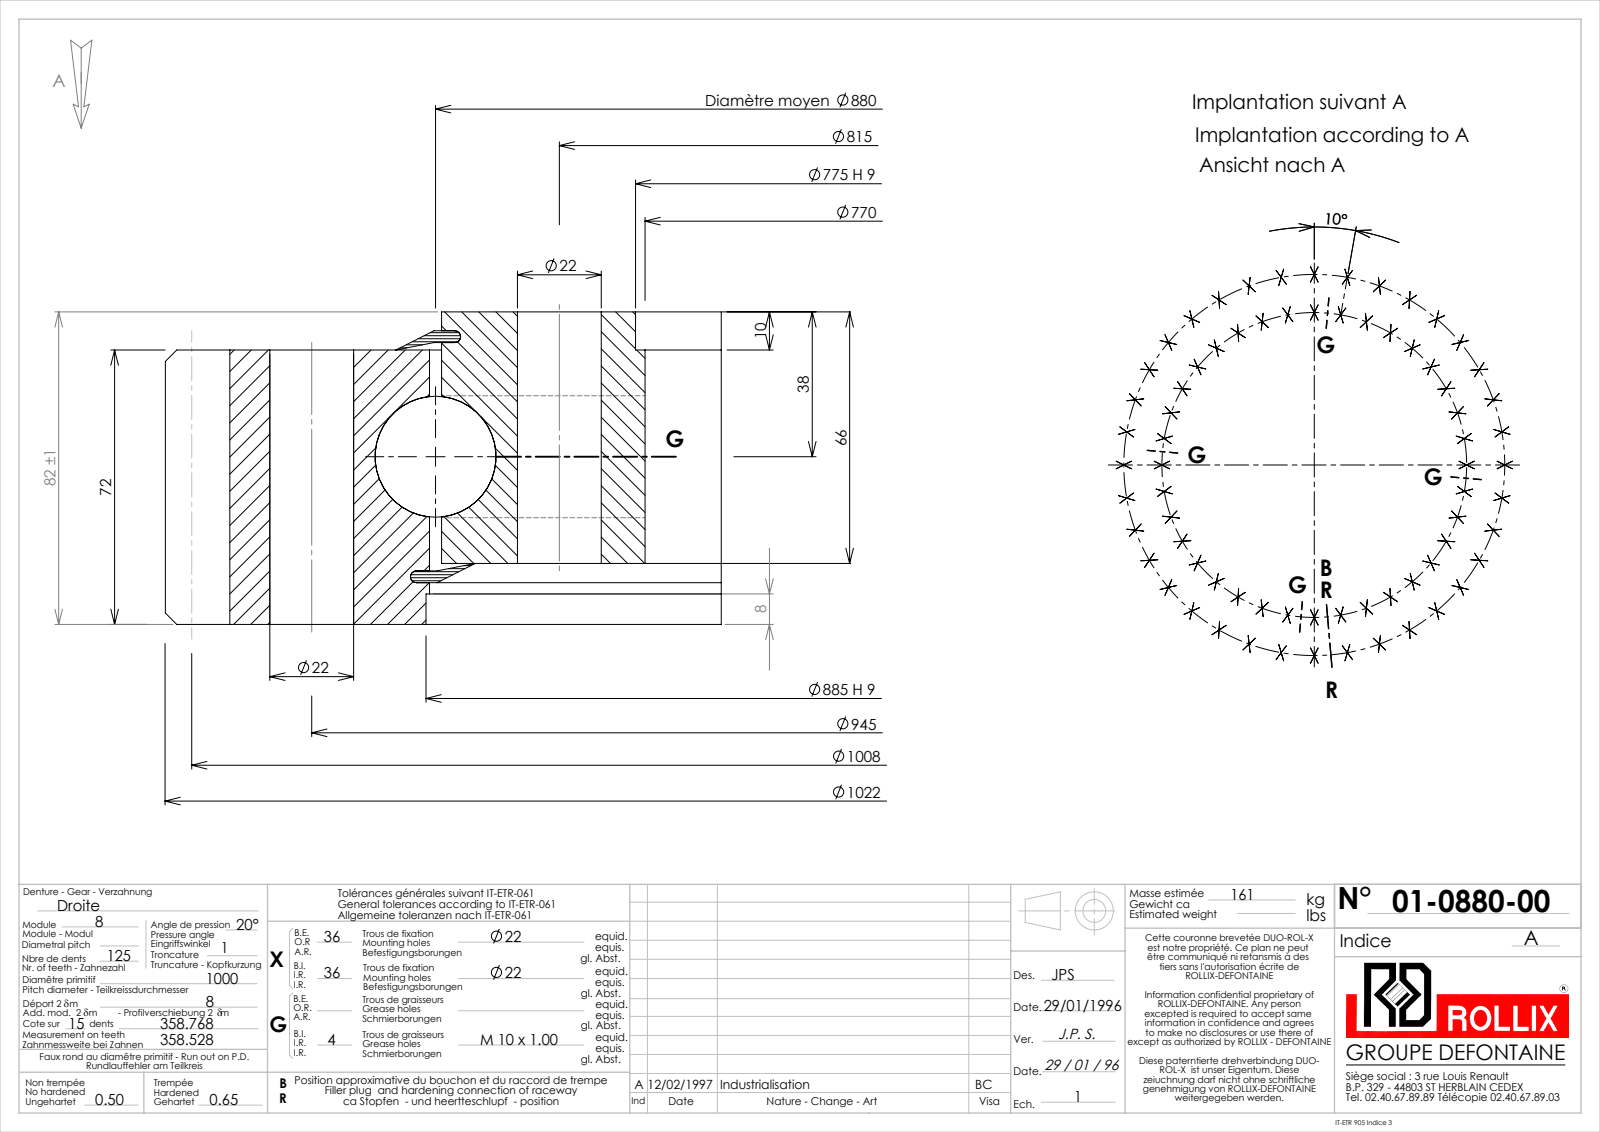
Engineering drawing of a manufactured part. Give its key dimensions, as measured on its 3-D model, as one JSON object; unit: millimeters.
{"part_name": "01-0880-00", "step_written_by": "SolidWorks 2016 (CONFIG_CONTROL_DESIGN)", "units": "millimeters", "bodies": {"solids": 5, "faces": 964, "planar": 264, "cylindrical": 421, "other": 279}, "overall_size": [1021.99, 1021.92, 82], "volume_mm3": 18540000, "surface_area_mm2": 2256000, "round_holes": [[22, 72], [9, 4], [770, 1], [775, 1], [883.17, 1], [885, 1]], "round_bosses_or_shafts": [[876.83, 1]], "partial_cylinders_radius": [[494, 1], [511, 1]], "face_to_face_distances": [72, 16, 56, 82, 66, 10, 5.05, 61.05, 1.95, 57.95], "hole_center_spacings": [82.36, 472.5, 542.03, 323.21, 912.8, 244.58, 164.1, 856.46]}
